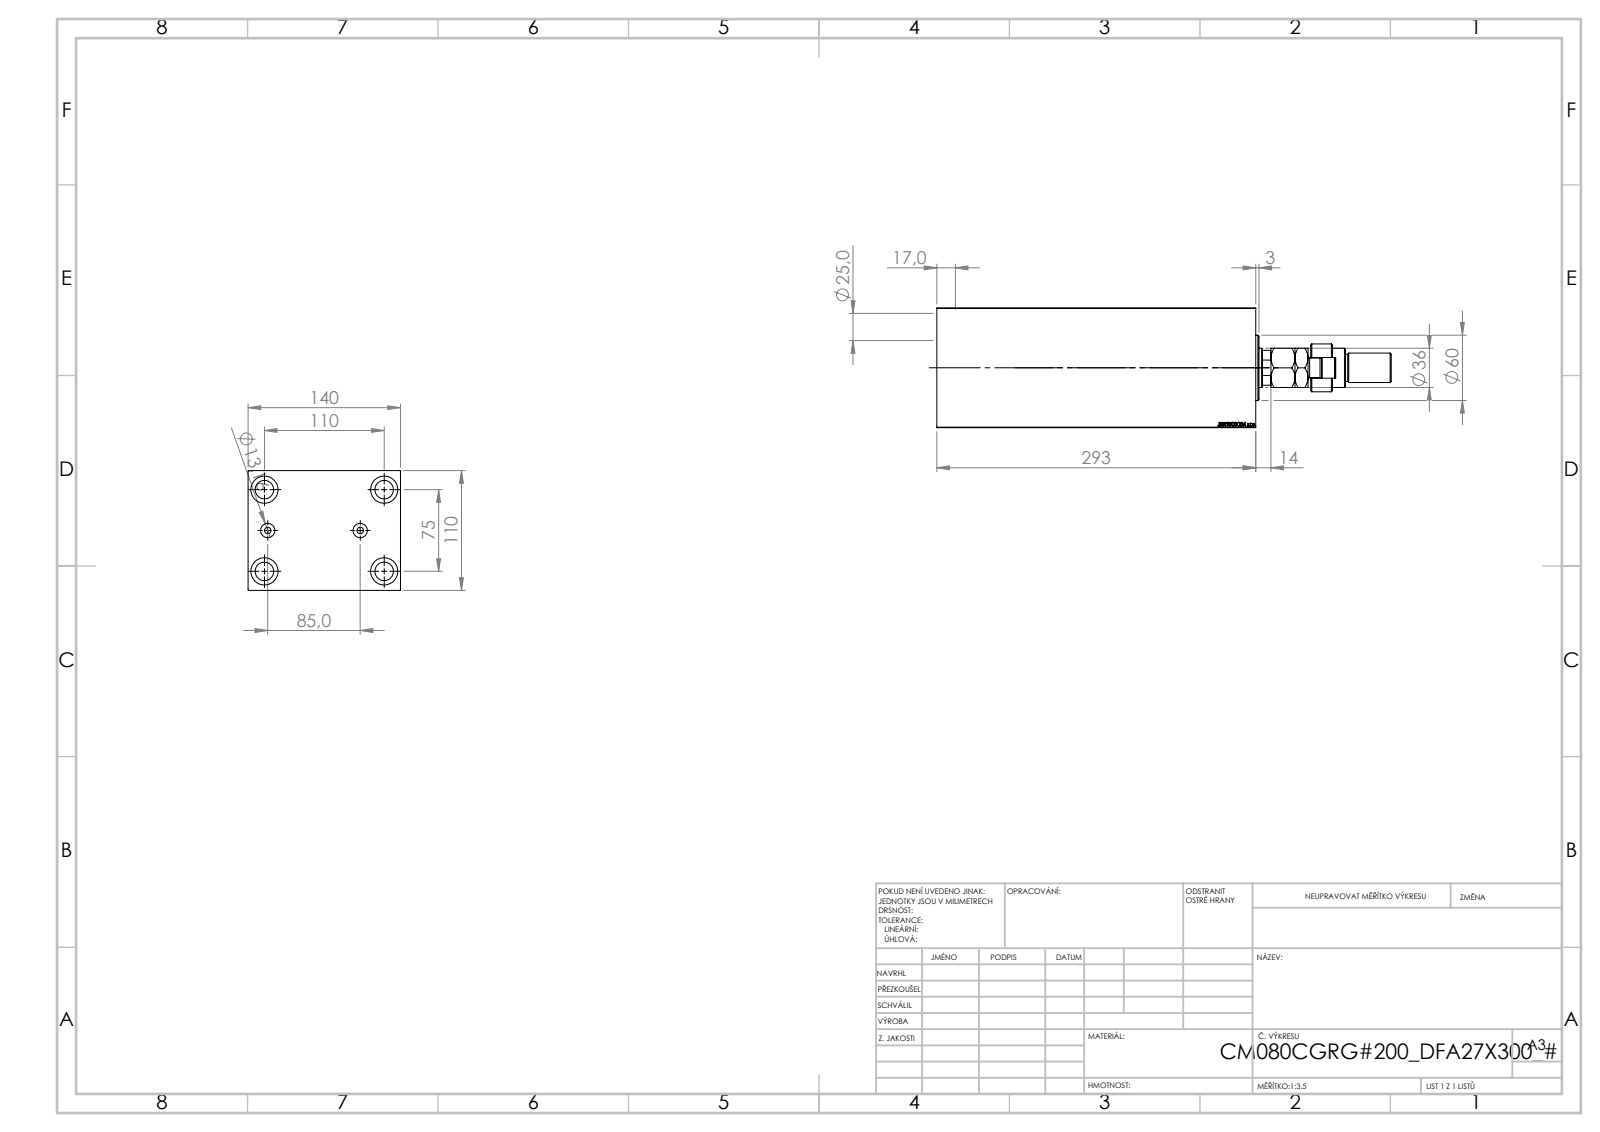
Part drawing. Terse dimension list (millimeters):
name: FEMALE_PART_FOR_DFA; MFA; V450CM_C_VCP; V450CM_VC_B (+1 more)
written by: SolidWorks 2019 (CONFIG_CONTROL_DESIGN)
unit: mm
bodies: 5 solids, 948 faces (439 planar, 71 cylindrical, 438 other)
size: 417.5 × 140 × 110
volume: 3 490 000 mm³; area: 412 654 mm²
holes: 4× ⌀17, 4× ⌀25, 2× ⌀6, 2× ⌀13.16, 1× ⌀25.5, 1× ⌀39.5, 1× ⌀80, 1× ⌀82, 1× ⌀87
bosses: 1× ⌀60, 1× ⌀44, 1× ⌀36, 1× ⌀28, 1× ⌀27, 1× ⌀25, 1× ⌀18
rounds: 1× R9.5, 1× R15, 1× R17.5
face distances: 110, 140, 293, 272, 21, 37.3, 234.7, 255.7, 237.3, 200
hole spacings: 39.53, 66.57, 104.46, 42.5, 75, 110, 133.14, 85
